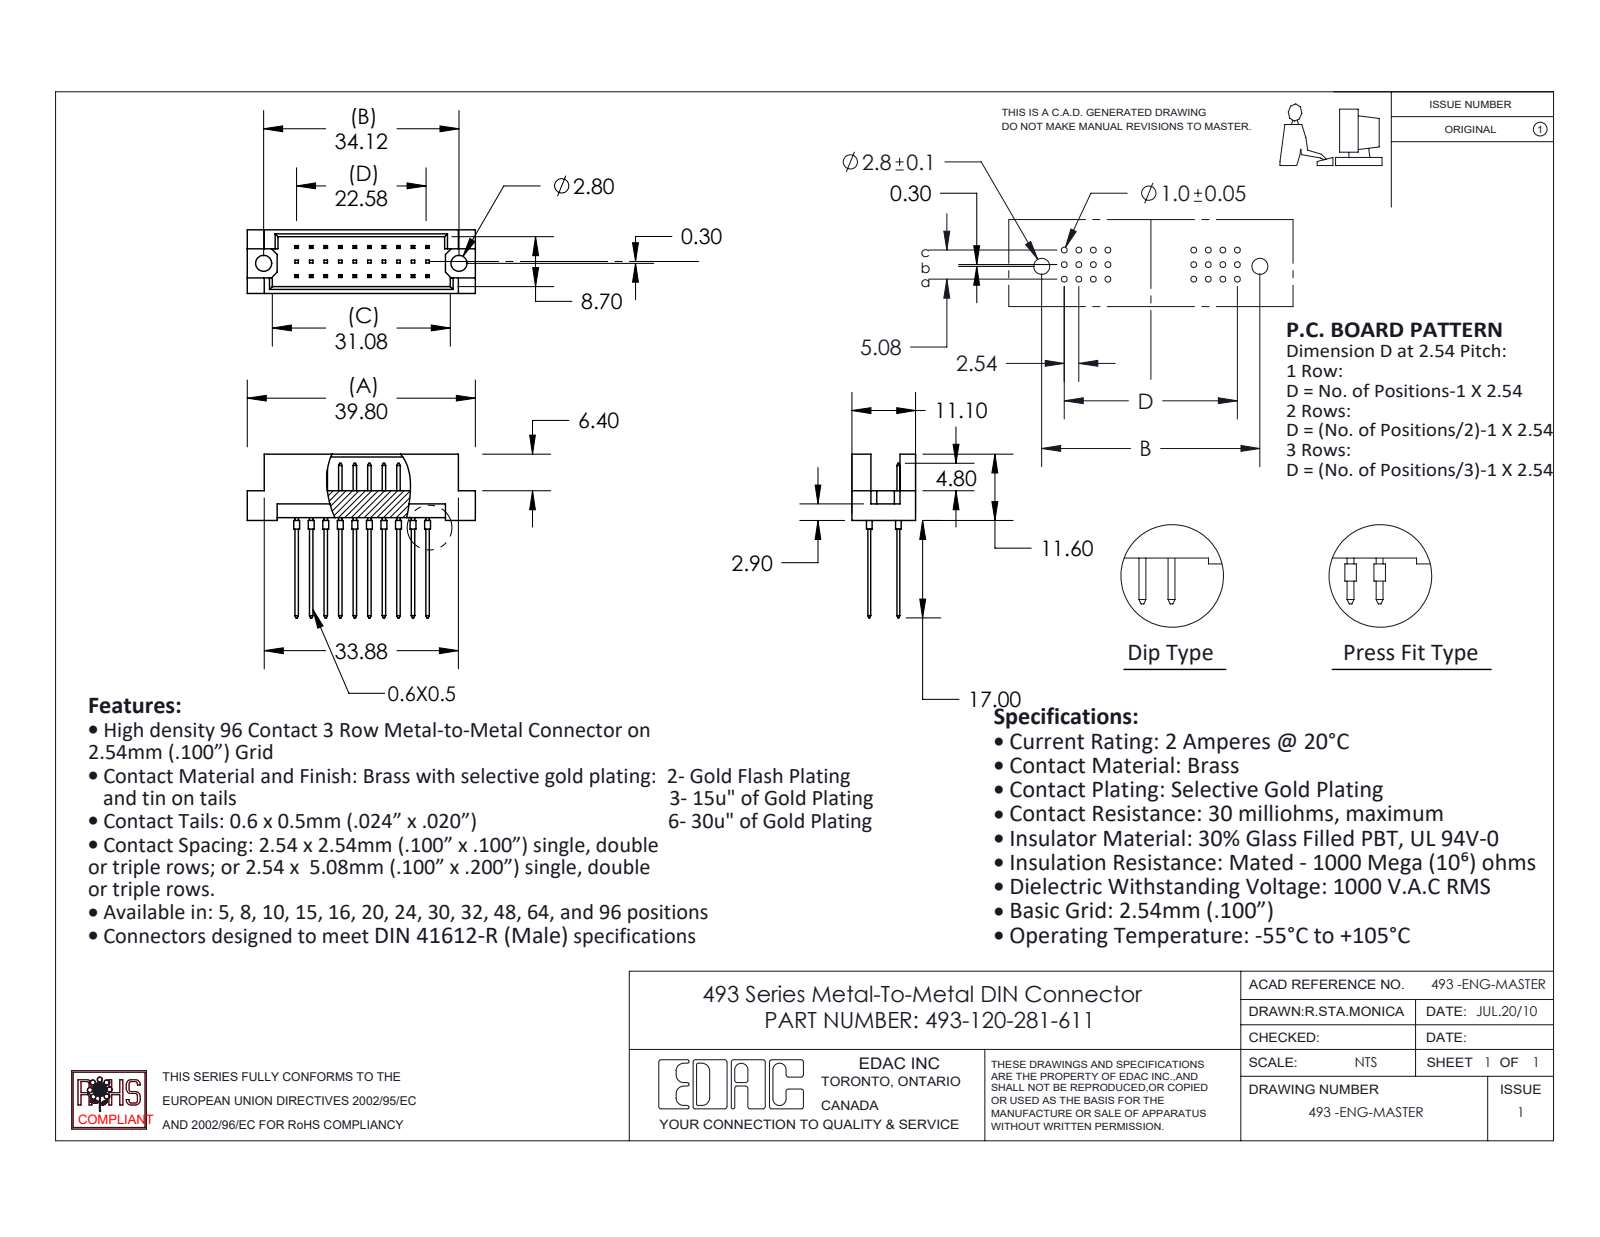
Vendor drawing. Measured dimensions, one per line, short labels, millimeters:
name: 493 Part_30; 493-124-281-321; 493-290_81
written by: SolidWorks 2020 (CONFIG_CONTROL_DESIGN)
unit: mm
bodies: 21 solids, 612 faces (568 planar, 44 cylindrical, 0 other)
size: 39.8 × 28.6 × 11.1
volume: 2 547 mm³; area: 3 966 mm²
holes: 2× ⌀2.8
bosses: 20× ⌀1
face distances: 5.08, 2.54, 1.2, 9.9, 0.5, 11.1, 2.76, 3.26, 7.84, 8.34
hole spacings: 34.12
